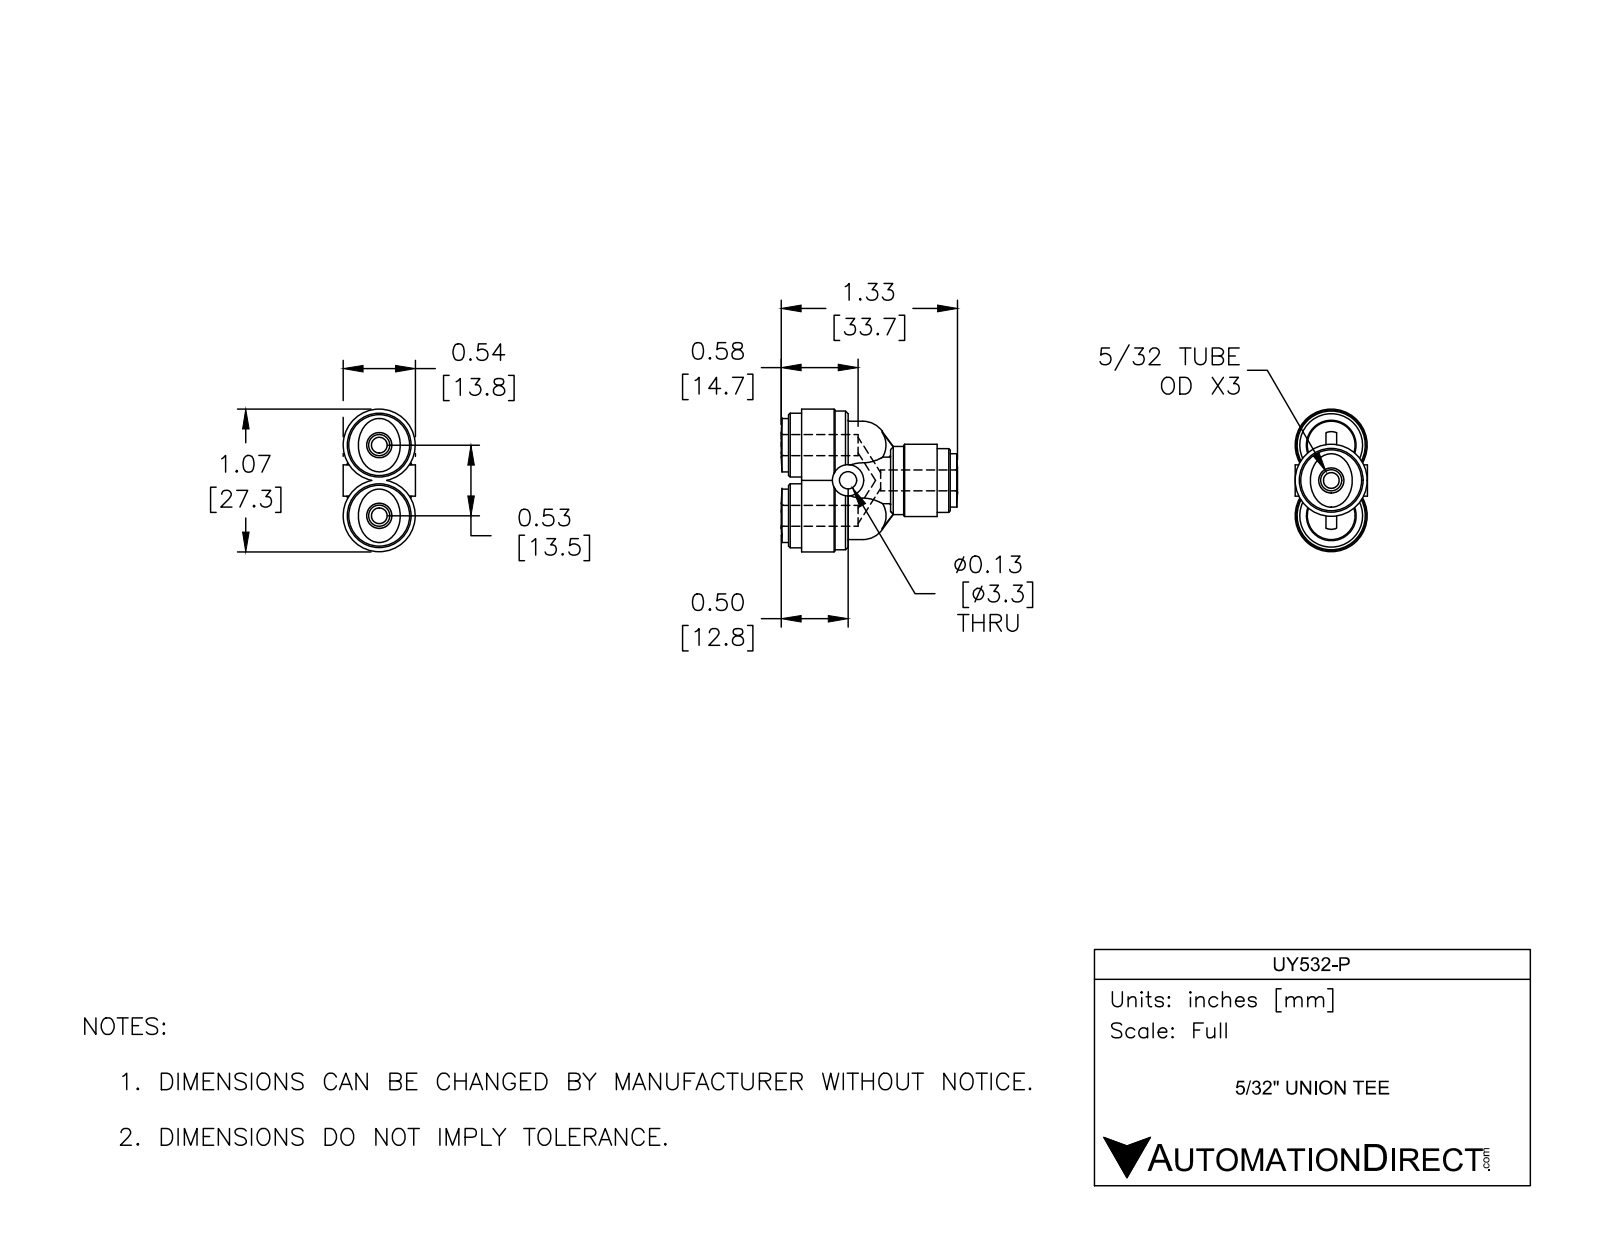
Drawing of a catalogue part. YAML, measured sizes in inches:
part_name: "UY532-P"
step_written_by: "SolidWorks 2017 (AUTOMOTIVE_DESIGN)"
units: inches
bodies: {solids: 1, faces: 108, planar: 21, cylindrical: 34, other: 53}
overall_size: [1.327, 1.075, 0.543]
volume: 0.343
surface_area: 5.275
round_holes:
  - {diameter: 0.157, count: 3}
  - {diameter: 0.13, count: 1}
round_bosses_or_shafts:
  - {diameter: 0.543, count: 3}
  - {diameter: 0.48, count: 3}
  - {diameter: 0.358, count: 3}
  - {diameter: 0.512, count: 1}
  - {diameter: 0.236, count: 1}
partial_cylinders:
  - {radius: 0.256, count: 2}
face_to_face_distances: [0.098, 0.35, 0.449, 0.768, 1.118, 0.669, 1.217, 0.319, 1.02, 0.866]
hole_center_spacings: [0.266, 0.531]
